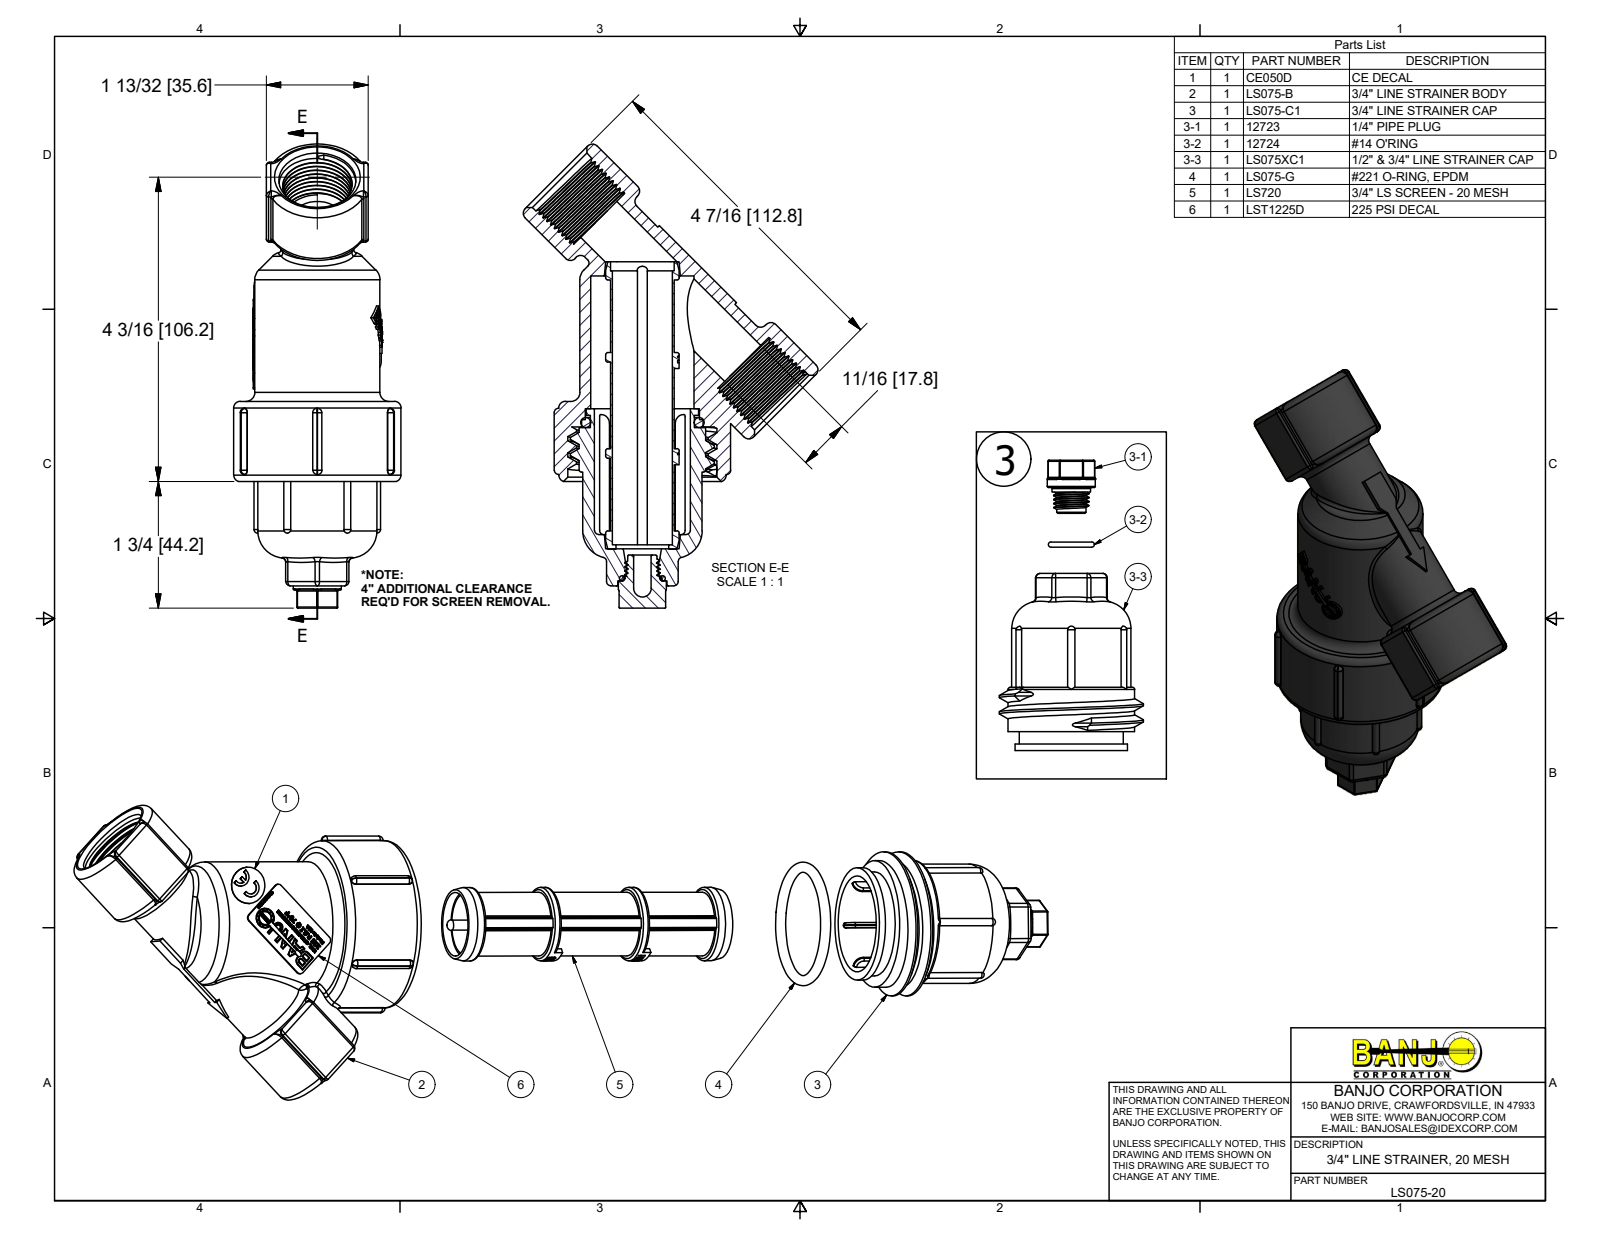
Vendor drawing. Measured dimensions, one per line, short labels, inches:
name: LS075-20; CE050D; LS075-B; LS075-C1 (+6 more)
written by: Autodesk Inventor 2018 (AUTOMOTIVE_DESIGN)
unit: in
bodies: 8 solids, 2271 faces (1134 planar, 384 cylindrical, 753 other)
size: 21.064 × 21.064 × 2.3
volume: 17.38 in³; area: 584.5 in²
holes: 2× ⌀0.181, 2× ⌀0.257, 1× ⌀0.24, 1× ⌀0.675, 1× ⌀0.7, 1× ⌀0.725, 1× ⌀0.825, 1× ⌀1.32, 1× ⌀1.42, 1× ⌀1.57, 1× ⌀1.671, 1× ⌀1.809
bosses: 2× ⌀0.27, 1× ⌀2.3, 1× ⌀1.981, 1× ⌀1.74, 1× ⌀1.72, 1× ⌀1.64, 1× ⌀1.545, 1× ⌀1.43
rounds: 67× R0.06, 35× R0.03, 26× R0.015, 8× R0.125, 6× R0.05, 4× R0.026, 4× R0.033, 4× R0.063
face distances: 0.25, 1.4, 0.16, 1.56, 3.75, 0.07, 0.26, 2.085, 2.075, 1.825
hole spacings: 0.638
